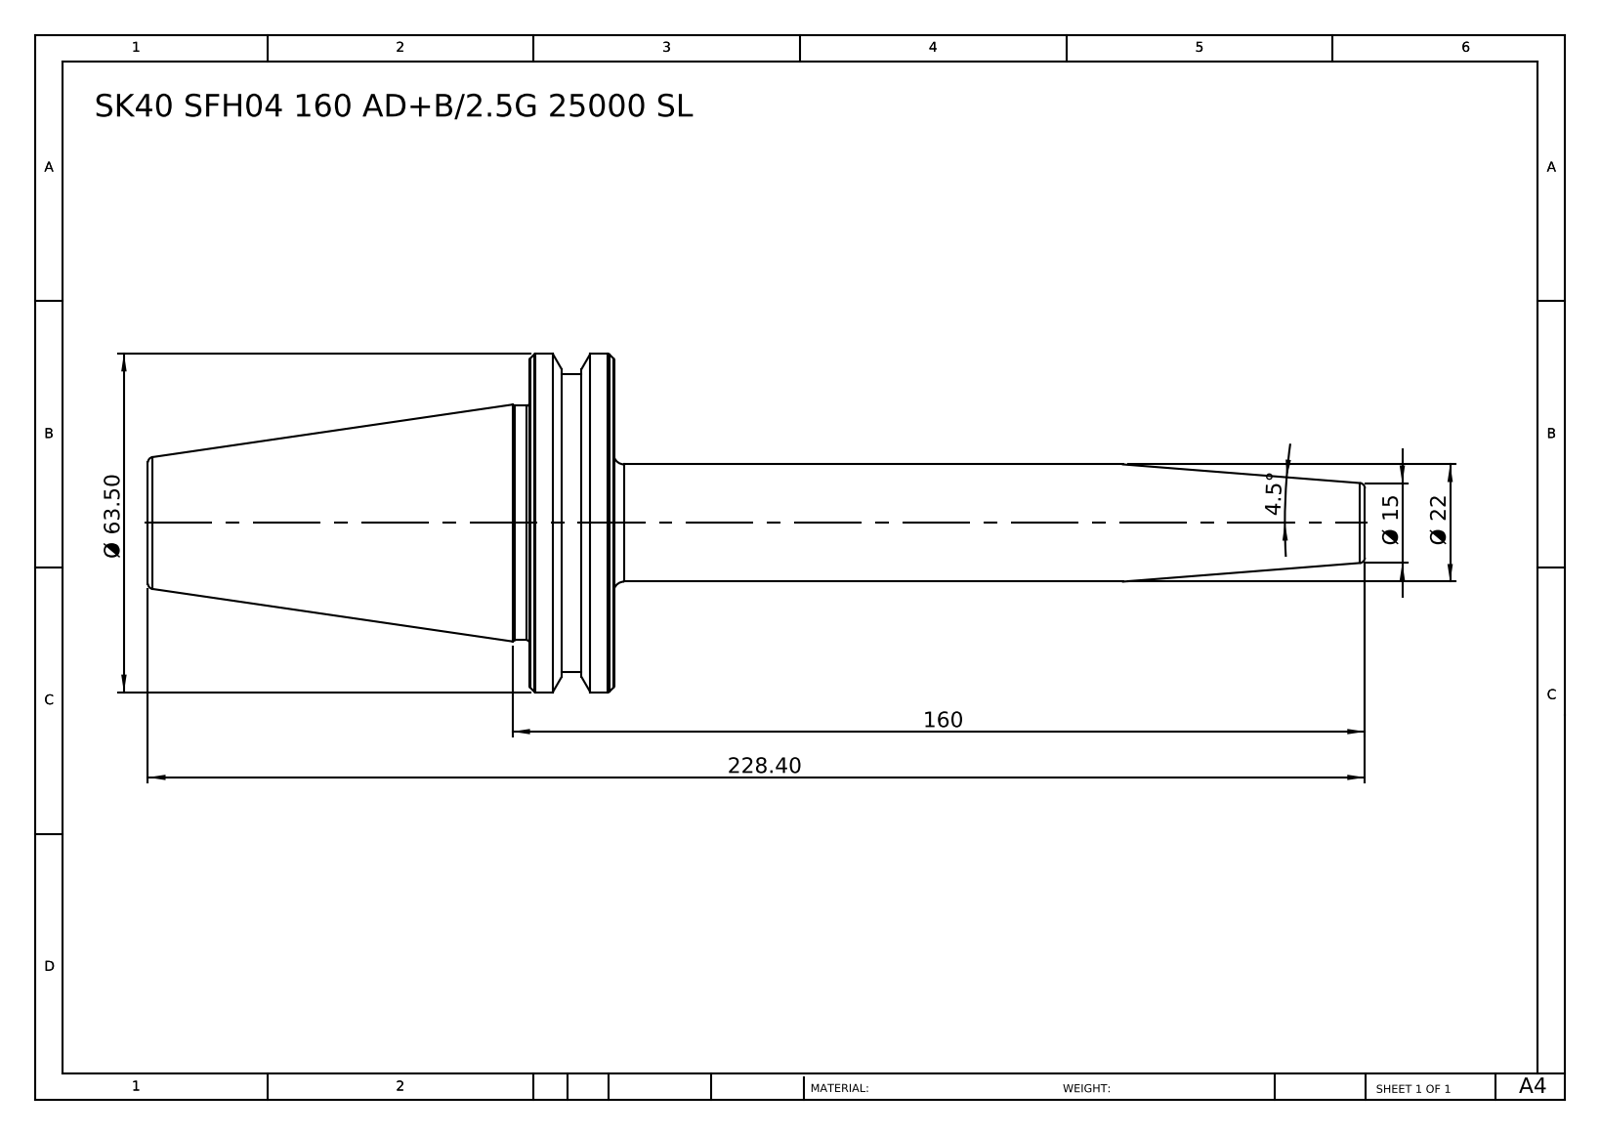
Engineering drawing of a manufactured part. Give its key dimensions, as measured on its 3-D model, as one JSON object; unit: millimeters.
{"part_name": "SK40 SFH04 160 AD+B-2.5G 25000 SL", "step_written_by": "SolidWorks 2014 (CONFIG_CONTROL_DESIGN)", "units": "millimeters", "bodies": {"solids": 1, "faces": 46, "planar": 6, "cylindrical": 10, "other": 30}, "overall_size": [228.4, 63.5, 63.5], "volume_mm3": 165700, "surface_area_mm2": 25889, "round_bosses_or_shafts": [[63.5, 1], [56, 1], [44, 1], [22, 1]], "face_to_face_distances": [15.9, 87.5, 71.6, 6.1, 9.8, 81.4, 9.9, 3.8, 6, 77.6]}
